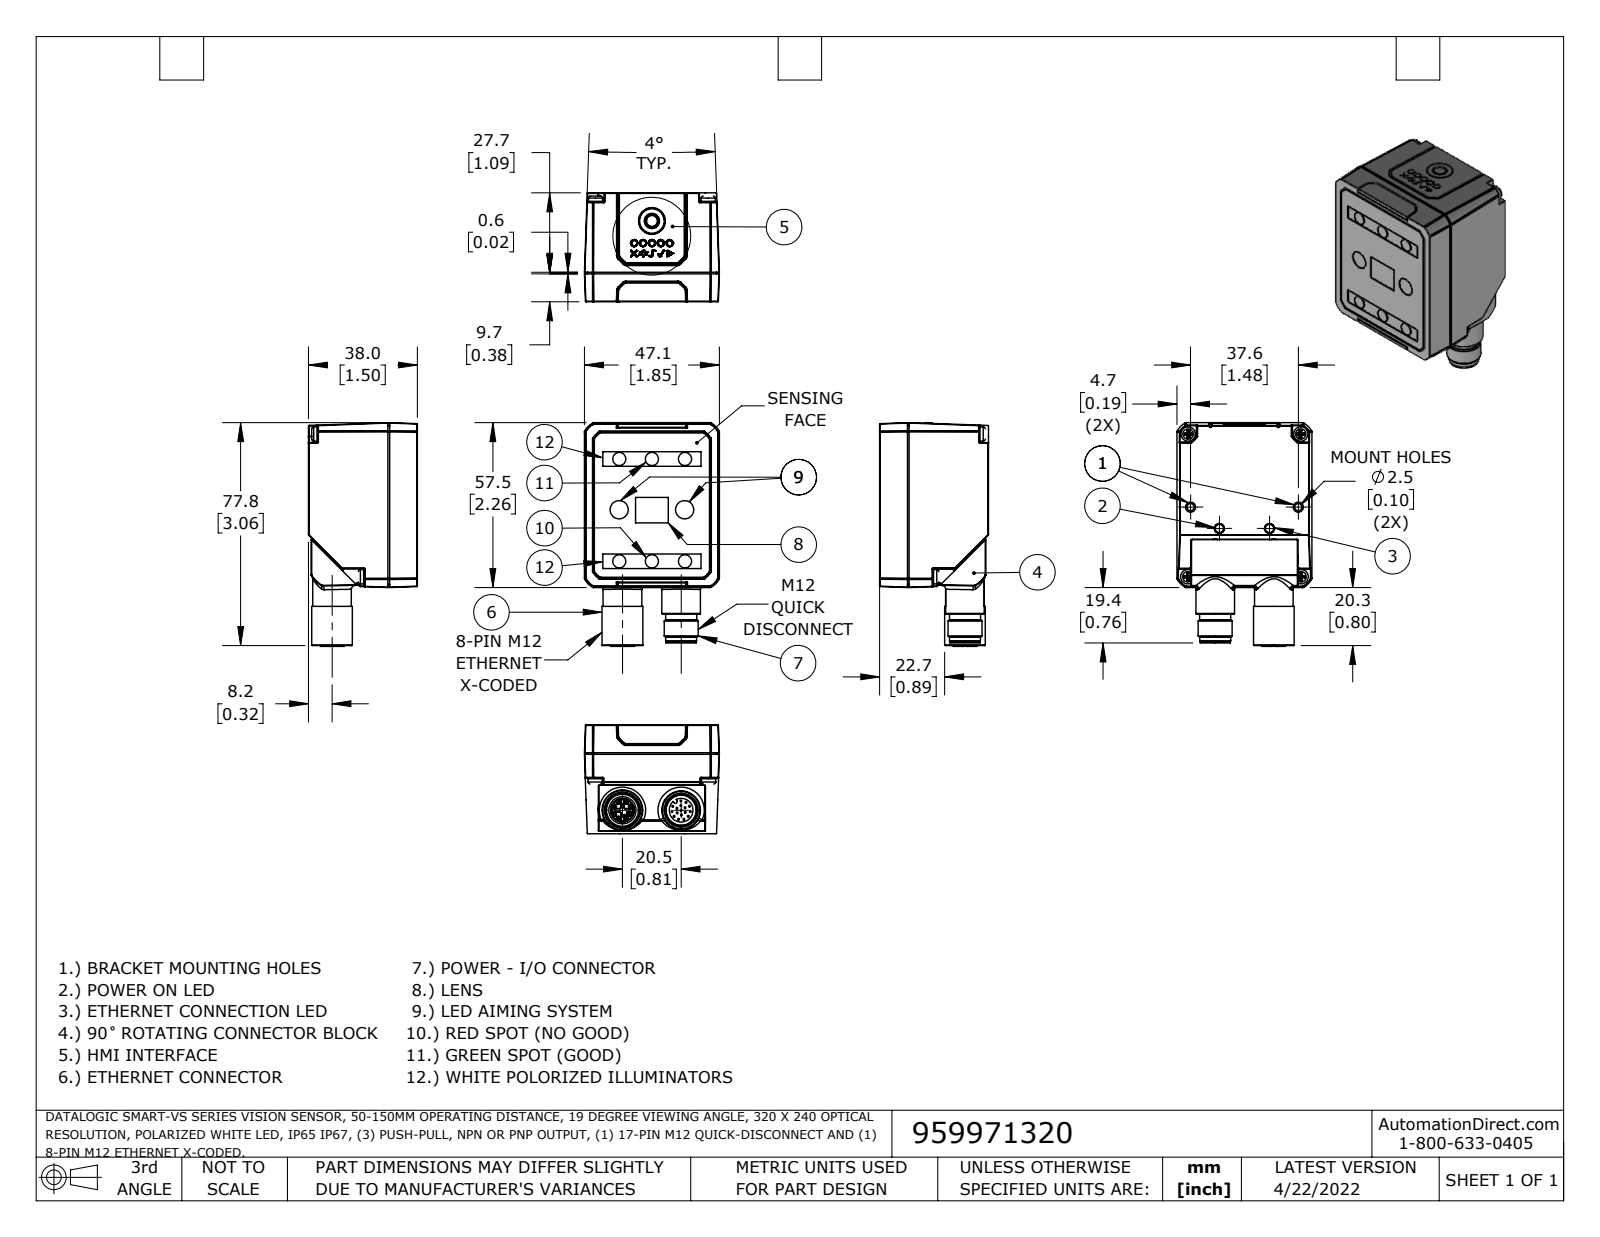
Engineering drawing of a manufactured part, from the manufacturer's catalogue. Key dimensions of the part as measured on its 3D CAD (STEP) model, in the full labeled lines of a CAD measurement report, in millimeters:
Part name (STEP PRODUCT): 959971320
STEP written by: SolidWorks 2021 (AUTOMOTIVE_DESIGN)
Units: millimetres
Bodies: 1 solid, 1129 faces (342 planar, 366 cylindrical, 421 other)
Overall size (bounding box): 78.1 × 47.1 × 38
Volume: 100 500 mm³ · Surface area: 18 220 mm²
Round holes (diameter × count): ⌀0.7 ×8, ⌀0.7 ×8, ⌀1.2 ×8, ⌀1.2 ×8, ⌀2.5 ×5, ⌀4.9 ×1, ⌀8.3 ×1, ⌀8.7 ×1, ⌀11.2 ×1, ⌀12.2 ×1
Round bosses / shafts (diameter × count): ⌀0.6 ×17, ⌀1.3 ×8, ⌀1.1 ×8, ⌀5 ×4, ⌀13.5 ×2, ⌀14.2 ×1, ⌀11.9 ×1, ⌀10.8 ×1
Partial cylindrical surfaces — rounded edges, fillets, slot ends (radius × count): R0.2 ×122, R0.4 ×17, R0.1 ×12, R1 ×9, R1 ×8, R2.8 ×8, R6.2 ×4, R7.3 ×4
Main face-to-face distances: 38, 0.9, 37.1, 27.7, 26.8, 10.3, 28.3, 27.4, 0.6, 9.7
Hole centre spacings: 3.1, 4.4, 2, 2.8, 3.1, 5.6, 5.9, 6.2
